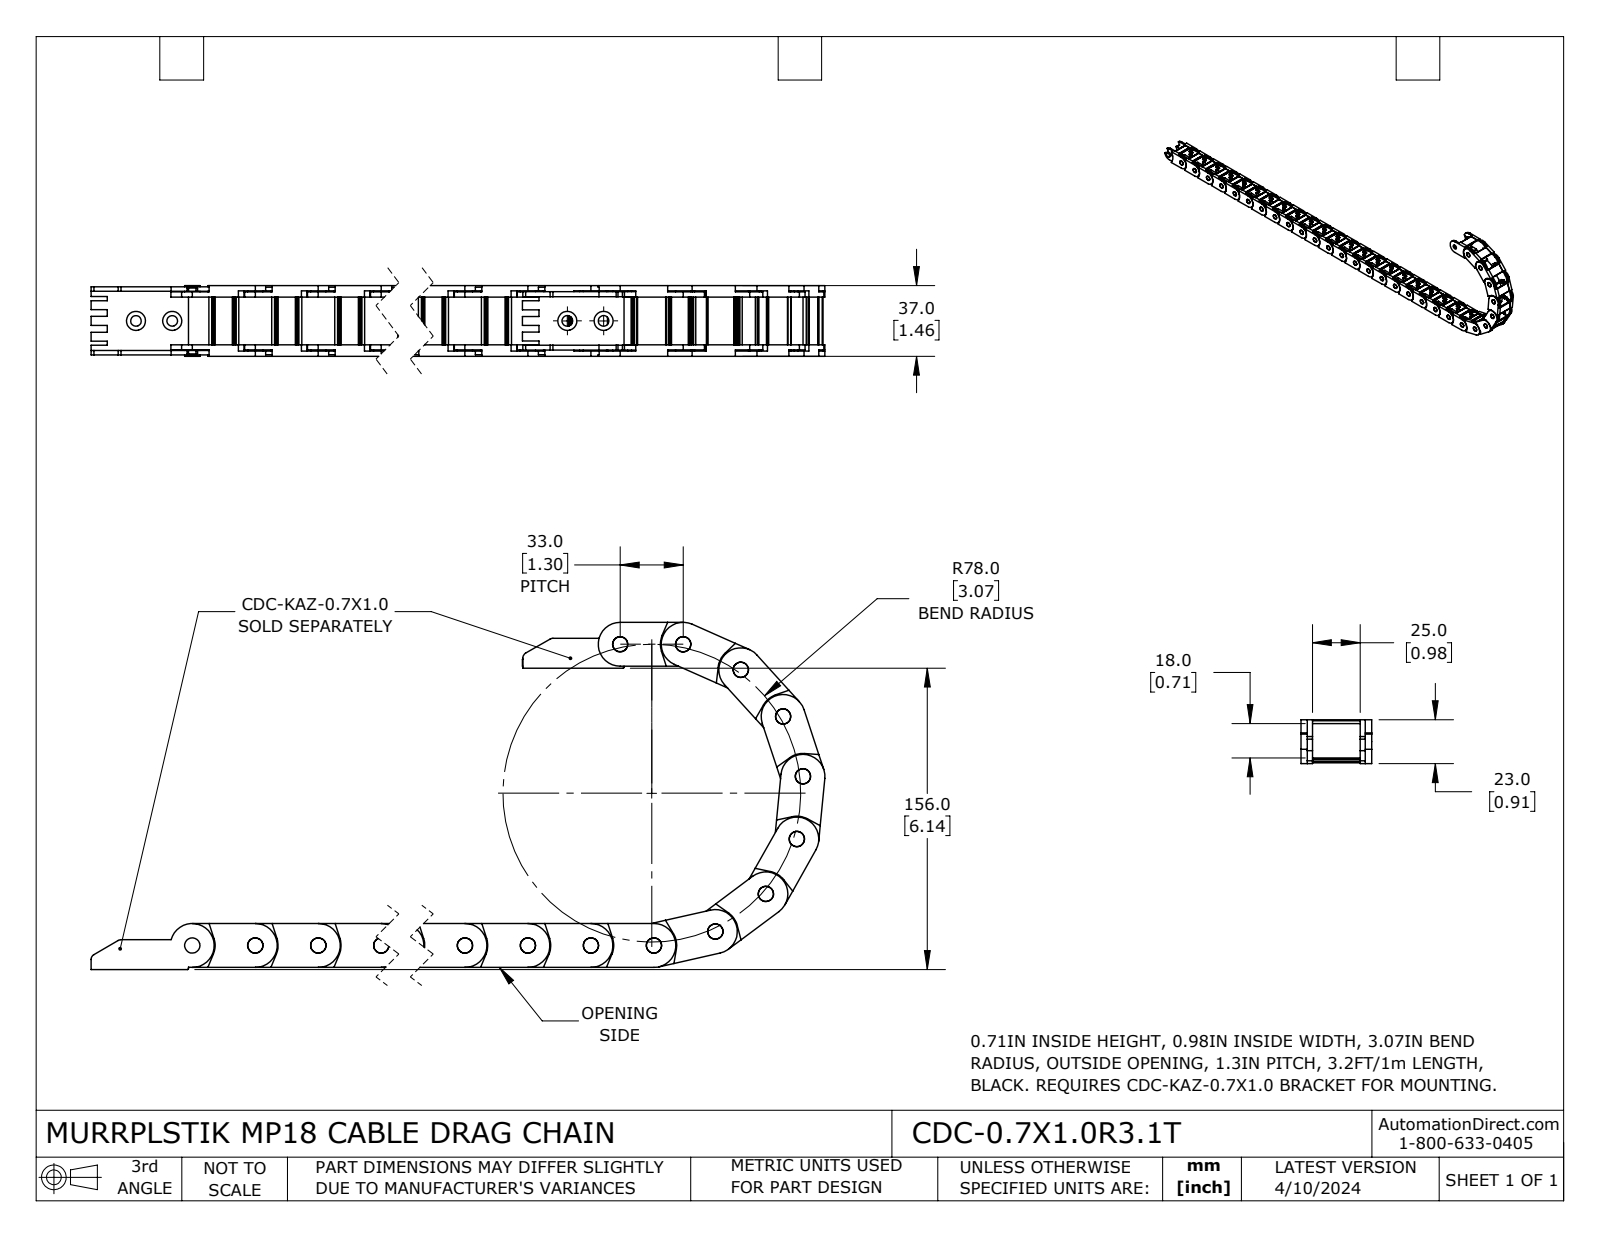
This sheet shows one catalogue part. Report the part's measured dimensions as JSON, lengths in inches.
{"part_name": "CDC-0.7X1.0R3.1T", "step_written_by": "SolidWorks 2023 (CONFIG_CONTROL_DESIGN)", "units": "inches", "bodies": {"solids": 30, "faces": 2490, "planar": 1290, "cylindrical": 1200, "other": 0}, "overall_size": [32.549, 7.115, 1.457], "volume_in3": 16.69, "surface_area_in2": 339.5, "round_holes": [[0.315, 30]], "round_bosses_or_shafts": [[0.315, 1]], "partial_cylinders_radius": [[0.02, 120], [0.059, 120], [0.008, 60], [0.012, 60], [0.453, 31], [0.47, 31], [0.197, 30], [0.215, 30]], "face_to_face_distances": [1.22, 0.106, 0.13, 0.236, 1.457, 1.327, 1.091, 0.984, 1.35, 0.024], "hole_center_spacings": [1.299, 2.598, 3.898, 5.197, 6.496, 7.795, 9.094, 10.394]}
